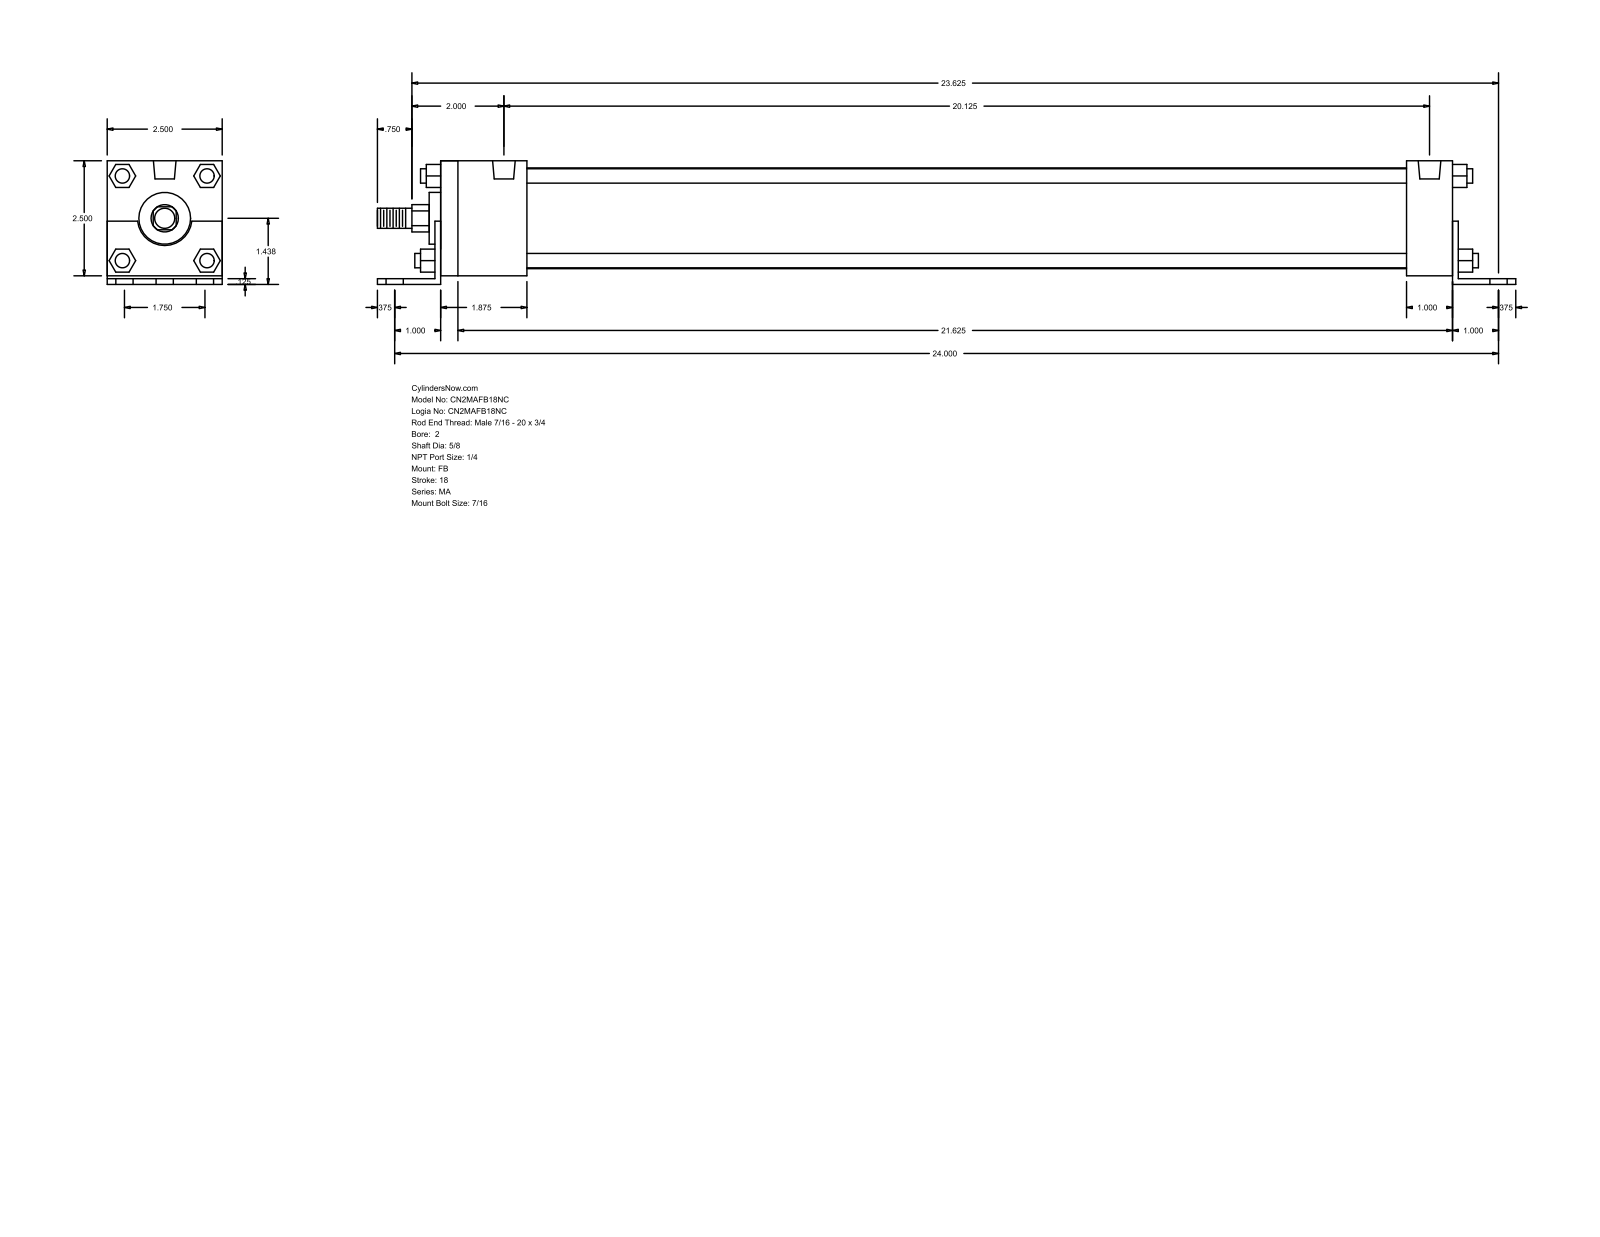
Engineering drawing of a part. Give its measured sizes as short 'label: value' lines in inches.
name: MA_FB__0200_0.625
written by: GSSL Pune (CONFIG_CONTROL_DESIGN)
unit: in
bodies: 0 solids, 140 faces (105 planar, 35 cylindrical, 0 other)
size: 24.75 × 2.687 × 2.5
holes: 6× ⌀0.437, 4× ⌀0.313, 2× ⌀0.492
bosses: 4× ⌀0.313, 1× ⌀2.19, 1× ⌀1.125, 1× ⌀0.625, 1× ⌀0.437
rounds: 1× R0.297, 1× R0.593
face distances: 2.5, 0.187, 0.125, 2.687, 0.063, 0.125, 2.563, 22.125, 22, 1.125
hole spacings: 0.875, 24.017, 24, 1.737, 1.75, 2.531, 20.125, 21.643
